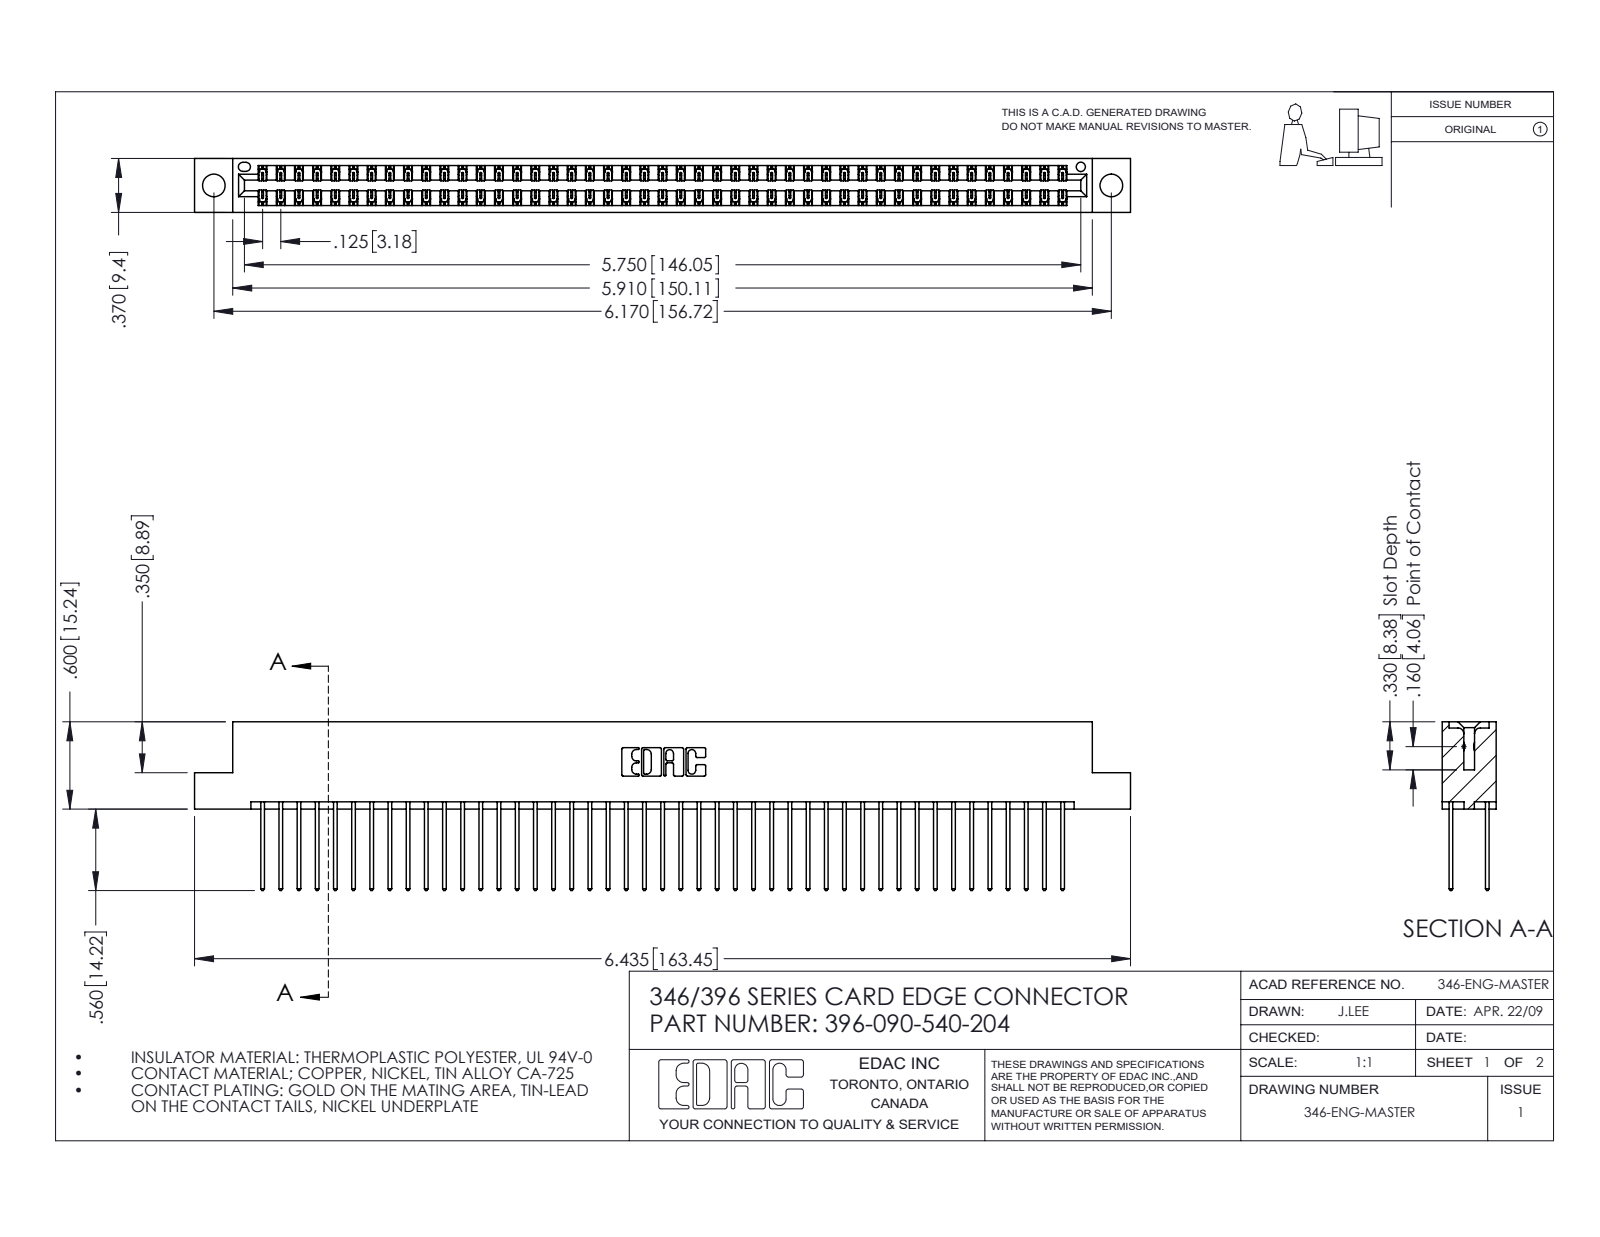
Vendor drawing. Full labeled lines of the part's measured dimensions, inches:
Part name (STEP PRODUCT): 346 Part_Flush Mounting Lugs - 0.156 Dia-TH; 345-292-001_345-293-140; 396-090-540-204
STEP written by: SolidWorks 2016 (CONFIG_CONTROL_DESIGN)
Units: inches
Bodies: 91 solids, 4802 faces (3226 planar, 1576 cylindrical, 0 other)
Overall size (bounding box): 6.435 × 1.16 × 0.37
Volume: 0.989 in³ · Surface area: 36.83 in²
Round holes (diameter × count): ⌀0.156 ×2, ⌀0.064 ×1
Partial cylindrical surfaces — rounded edges, fillets, slot ends (radius × count): R0.006 ×135, R0.01 ×90, R0.01 ×22, R0.007 ×6, R0.031 ×6, R0.026 ×3, R0.014 ×2, R0.022 ×2
Main face-to-face distances: 0.048, 0.322, 0.25, 0.072, 0.298, 0.025, 0.37, 0.275, 0.148, 0.222
Hole centre spacings: 0.246, 5.961, 6.17
